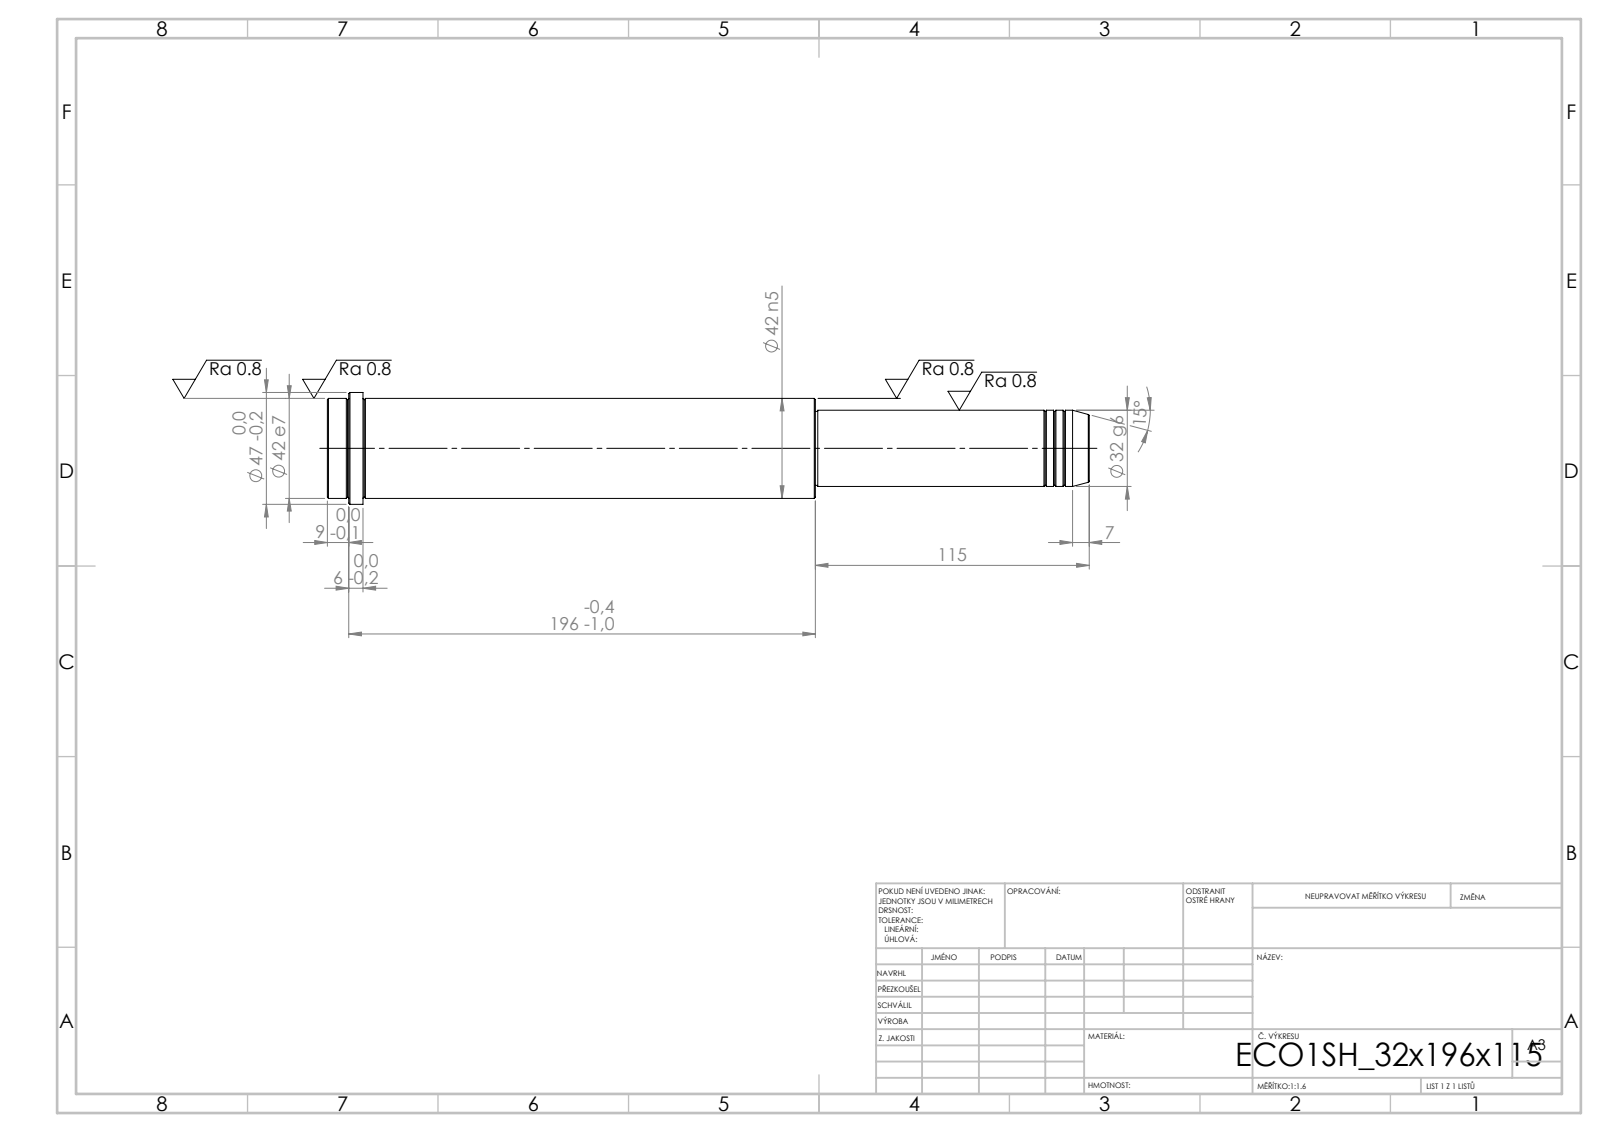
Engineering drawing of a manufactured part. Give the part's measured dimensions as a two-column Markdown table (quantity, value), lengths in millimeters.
| quantity | value |
| --- | --- |
| STEP written by | SolidWorks 2019 (CONFIG_CONTROL_DESIGN) |
| units | millimeters |
| bodies | 1 solid, 52 faces (6 planar, 16 cylindrical, 30 other) |
| overall size | 320 × 47 × 47 |
| volume | 377 645 mm³ |
| surface area | 42 250 mm² |
| round bosses / shafts (diameter × count) | 47 × 1, 42 × 1, 32 × 1, 31 × 1 |
| main face-to-face distances | 320, 115, 205, 305, 190, 15, 311, 196, 6, 9 |
